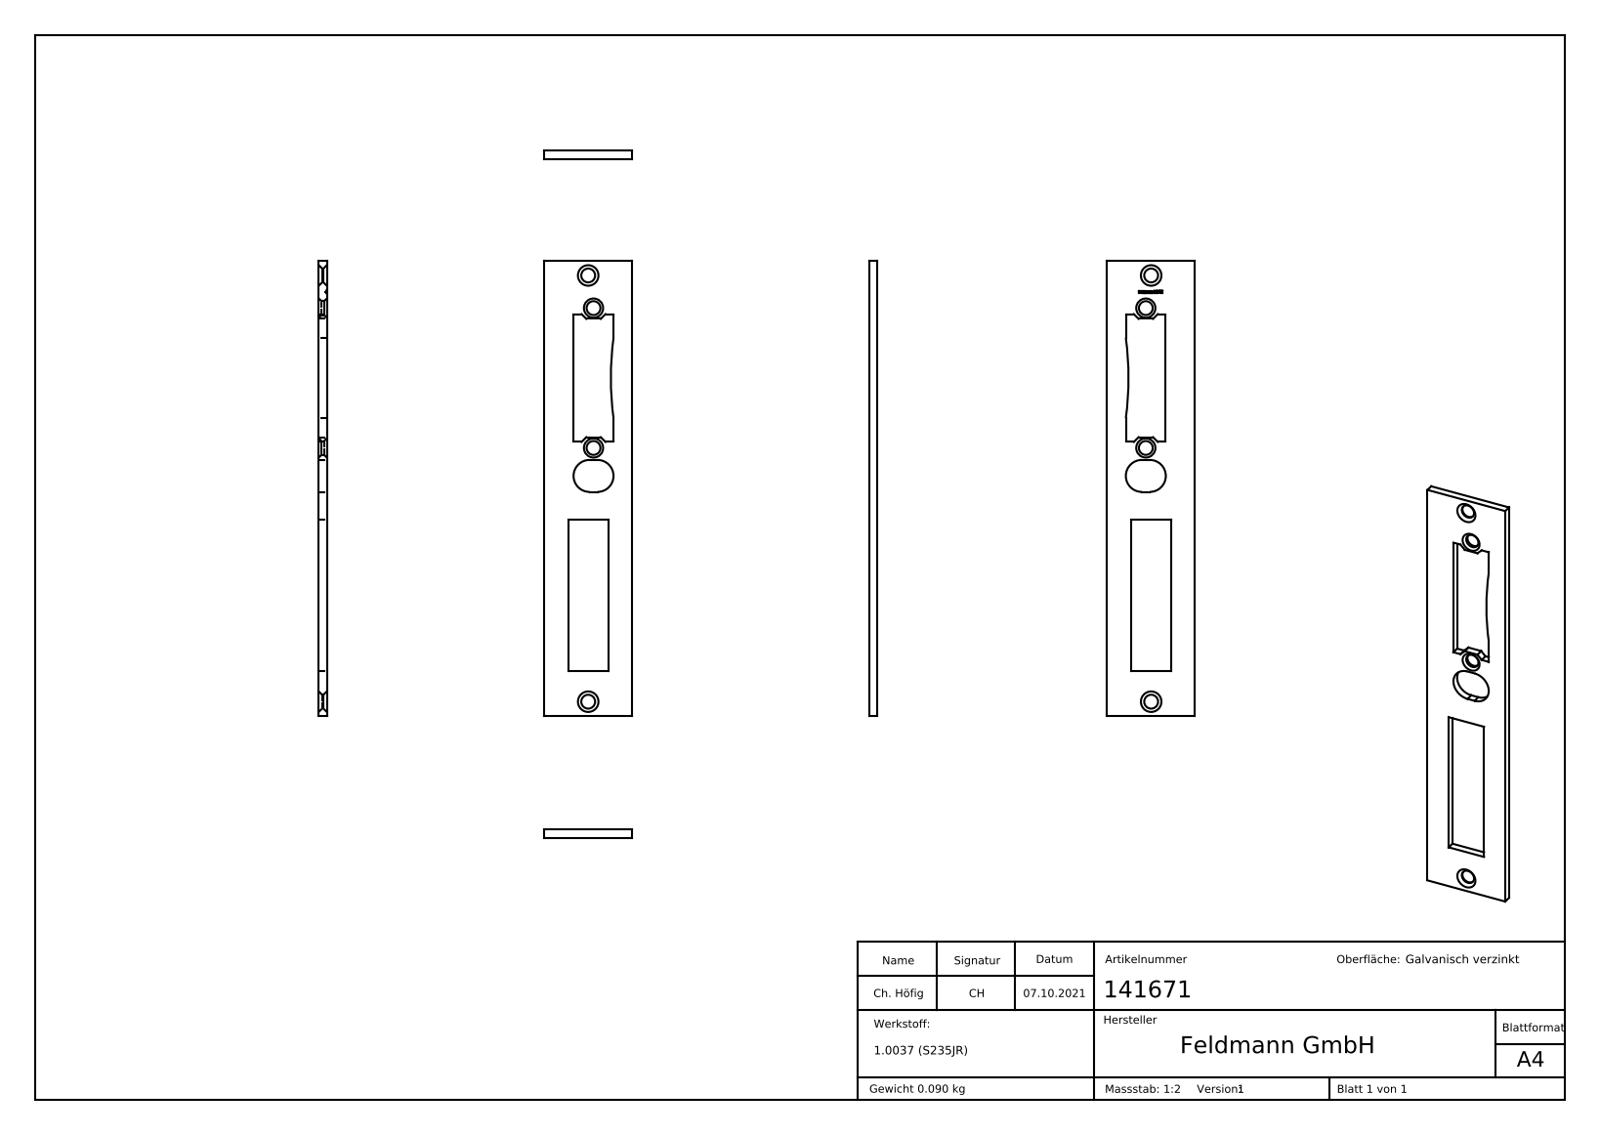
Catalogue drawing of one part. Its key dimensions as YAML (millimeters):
part_name: "141671"
step_written_by: "SolidWorks 2018 (CONFIG_CONTROL_DESIGN)"
units: millimeters
bodies: {solids: 1, faces: 210, planar: 138, cylindrical: 7, other: 65}
overall_size: [171, 33, 3]
volume: 11543
surface_area: 10079
round_holes:
  - {diameter: 5.2, count: 4}
partial_cylinders:
  - {radius: 6, count: 2}
  - {radius: 113, count: 1}
face_to_face_distances: [3, 33, 9, 24, 15, 2, 11, 13, 22, 17]
hole_center_spacings: [12.41, 52.5, 64.78, 95.27, 147.76, 160]
